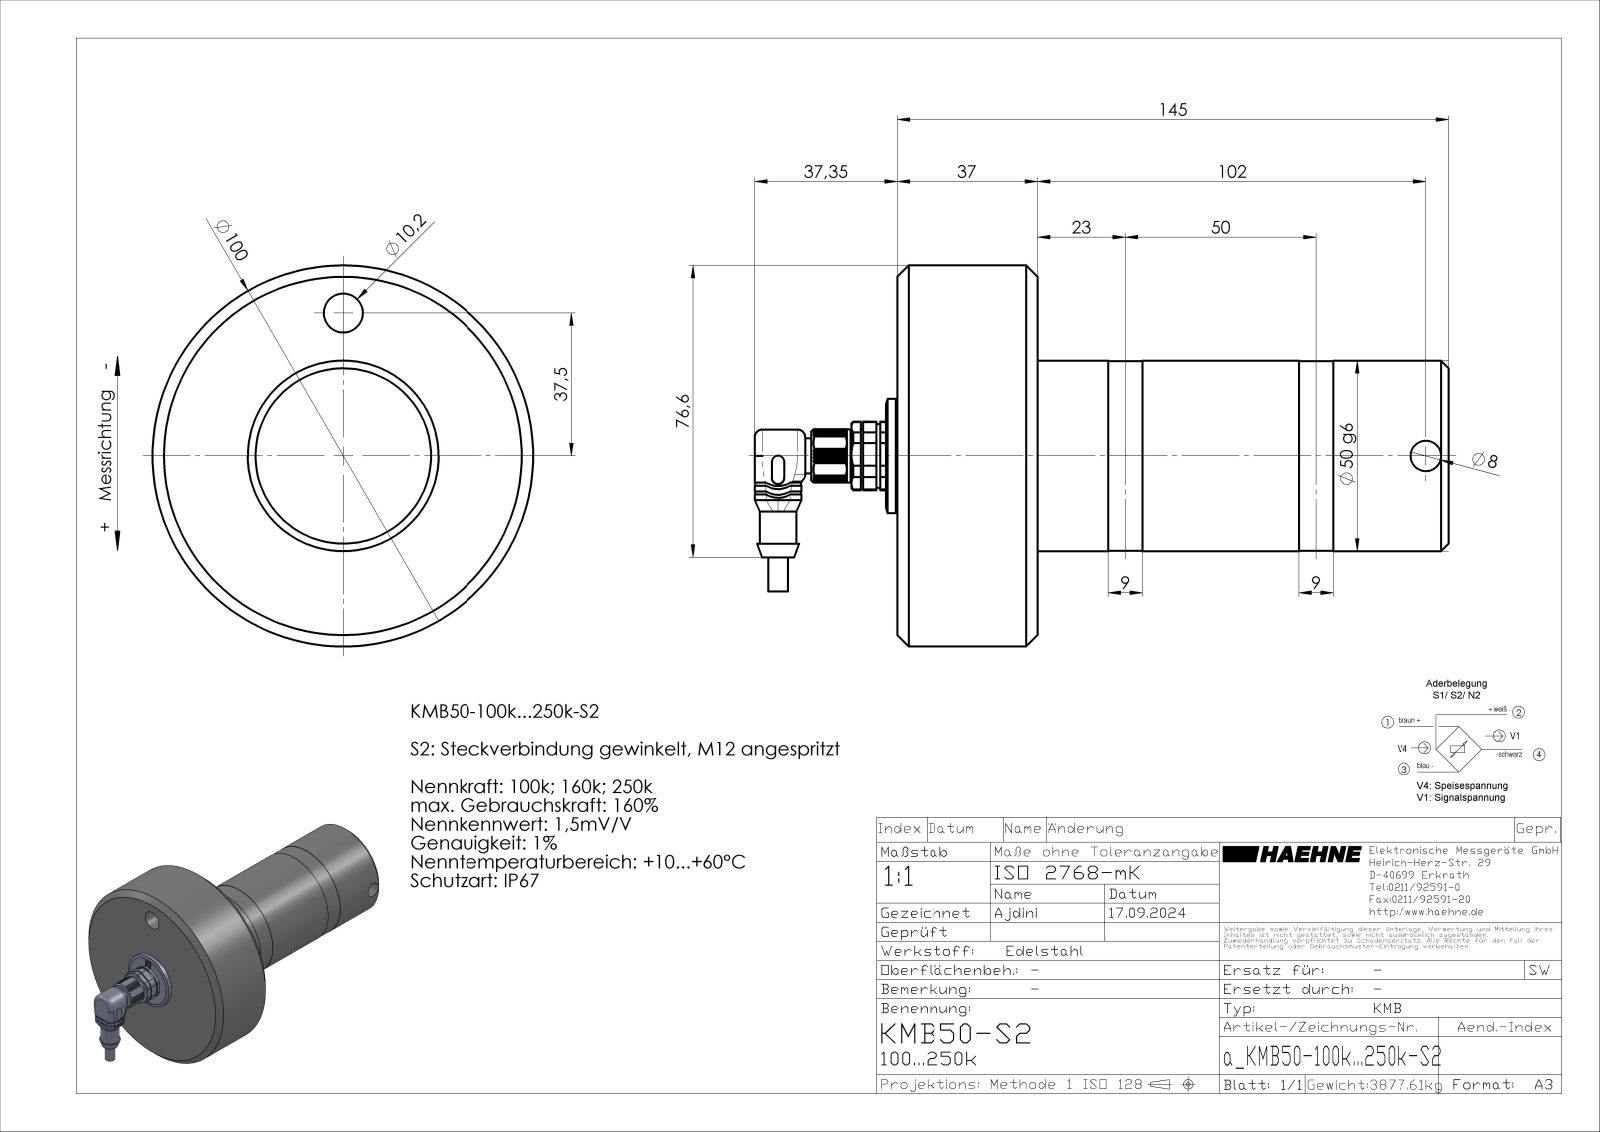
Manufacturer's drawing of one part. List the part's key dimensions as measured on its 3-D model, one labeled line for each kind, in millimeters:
Part name (STEP PRODUCT): a_KMB50-100k...250k-S2; a_KMB50-100k...150k-S2_Angebot; Option S2; X02045Z1 SKINDICHT MR-M 25x1,5 _ 16x1,5 Art_ Nr_ 52104313 (+2 more)
STEP written by: SolidWorks 2023 (CONFIG_CONTROL_DESIGN)
Units: millimetres
Bodies: 4 solids, 723 faces (386 planar, 190 cylindrical, 147 other)
Overall size (bounding box): 182.35 × 100 × 100
Volume: 500 332 mm³ · Surface area: 54 648 mm²
Round holes (diameter × count): ⌀1.22 ×5, ⌀1.1 ×4, ⌀1.15 ×4, ⌀1.6 ×4, ⌀1.85 ×4, ⌀1.2 ×1, ⌀8 ×1, ⌀8.37 ×1, ⌀8.42 ×1, ⌀9.3 ×1, ⌀10.2 ×1, ⌀10.8 ×1
Round bosses / shafts (diameter × count): ⌀1.8 ×4, ⌀1.55 ×4, ⌀1.5 ×4, ⌀1 ×4, ⌀100 ×1, ⌀50 ×1, ⌀49.8 ×1, ⌀30 ×1
Partial cylindrical surfaces — rounded edges, fillets, slot ends (radius × count): R0.2 ×16, R0.3 ×9, R0.4 ×4, R0.53 ×4, R1 ×4, R1.27 ×4, R6 ×4, R1.6 ×2
Main face-to-face distances: 37, 108, 145, 3, 148, 40, 2.5, 7, 12.05, 30
Hole centre spacings: 1.29, 2.09, 2.5, 3.54, 5, 8.65, 11.14, 13.63
